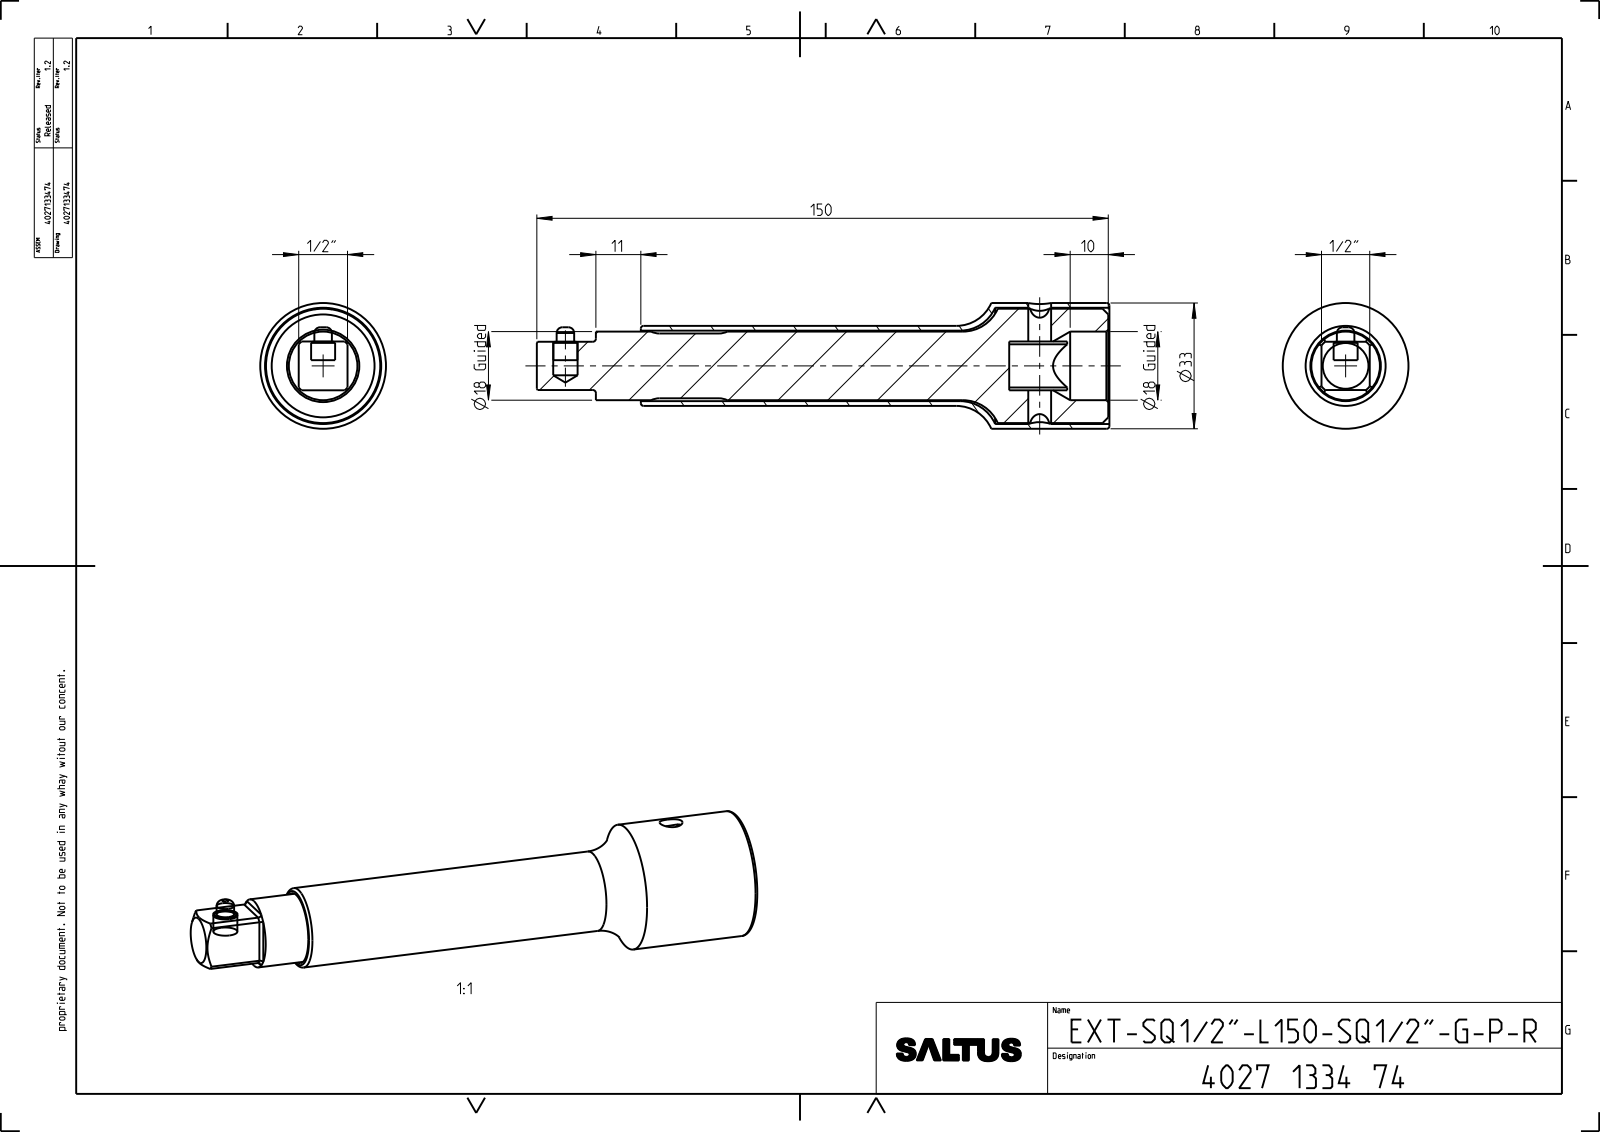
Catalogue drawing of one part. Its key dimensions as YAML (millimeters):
part_name: "4027133494; 4027299523; 4027133474_ASM"
step_written_by: "CREO PARAMETRIC BY PTC INC, 2022414 (CONFIG_CONTROL_DESIGN)"
units: millimeters
bodies: {solids: 2, faces: 101, planar: 20, cylindrical: 46, other: 35}
overall_size: [150.3, 33, 33]
volume: 55231
surface_area: 30763
round_holes:
  - {diameter: 6, count: 1}
  - {diameter: 6.4, count: 1}
  - {diameter: 18.5, count: 1}
  - {diameter: 30.5, count: 1}
round_bosses_or_shafts:
  - {diameter: 33, count: 1}
  - {diameter: 30, count: 1}
  - {diameter: 21, count: 1}
  - {diameter: 18, count: 1}
  - {diameter: 17, count: 1}
  - {diameter: 6.3, count: 1}
  - {diameter: 4.6, count: 1}
partial_cylinders:
  - {radius: 0.8, count: 4}
  - {radius: 8.3, count: 1}
  - {radius: 8.55, count: 1}
face_to_face_distances: [12.74, 12.66, 12.82, 26, 150, 124, 134.5, 108.5, 15.5, 26.3]
hole_center_spacings: [124.5]
